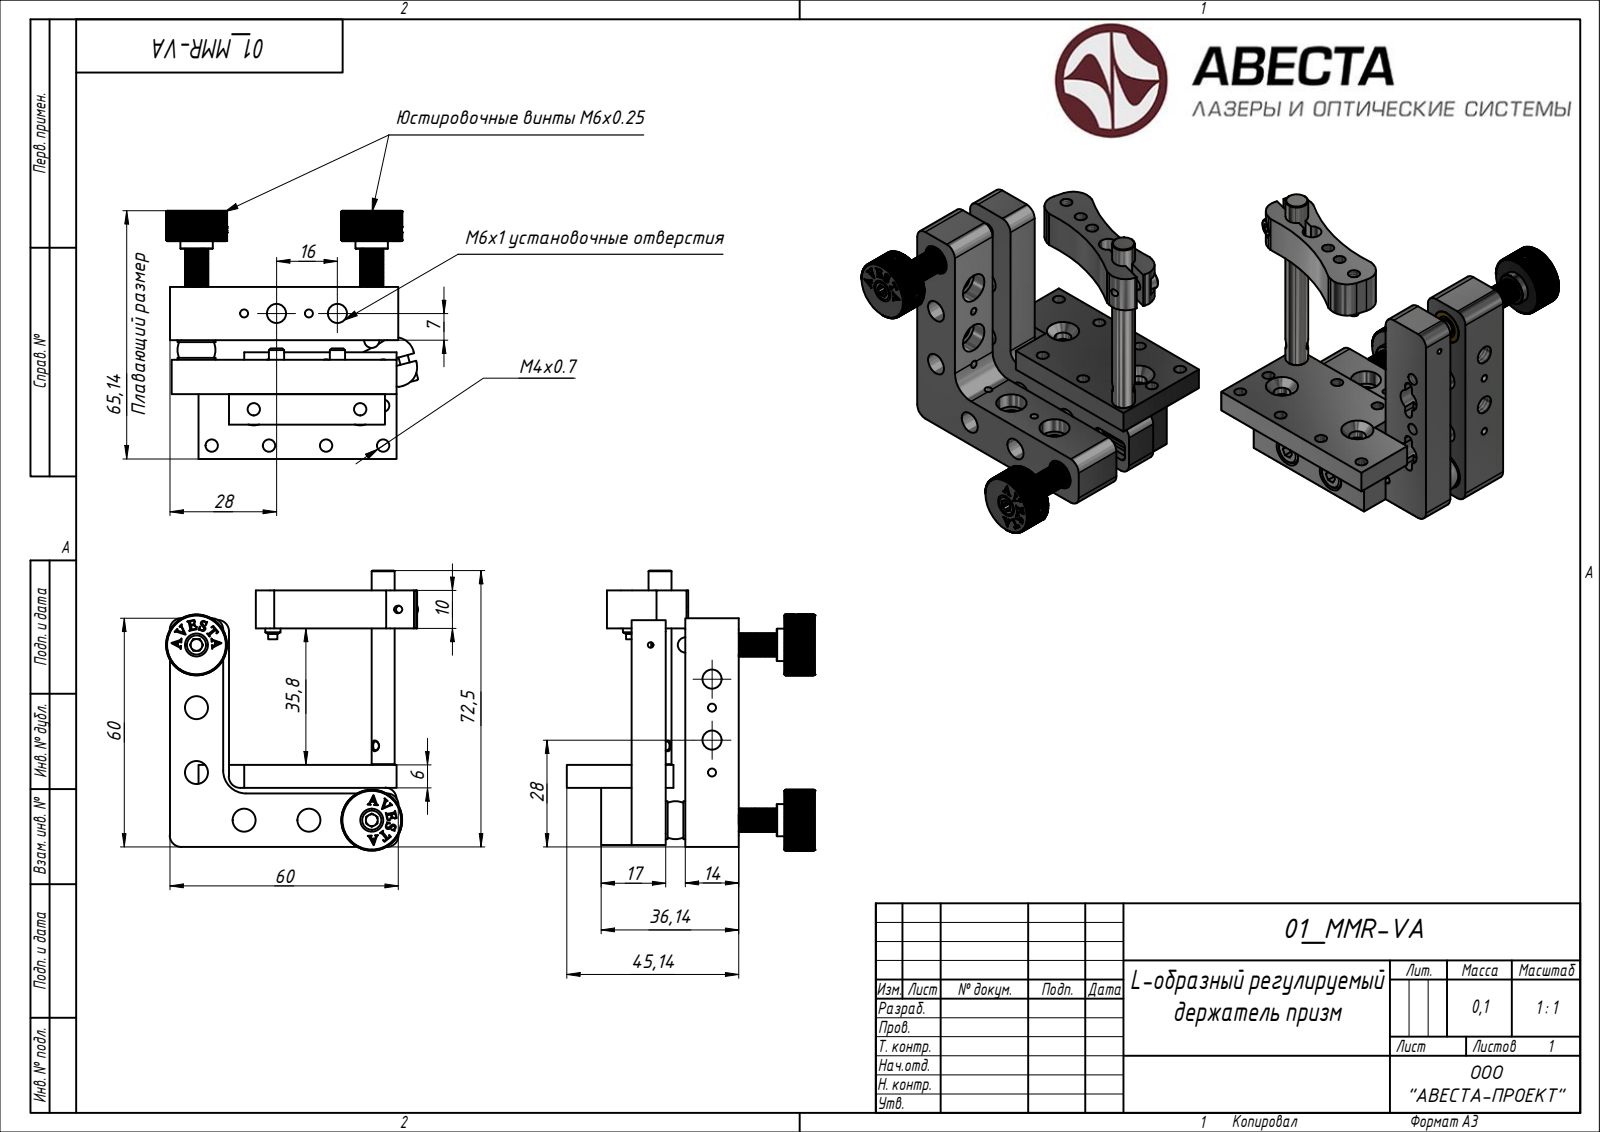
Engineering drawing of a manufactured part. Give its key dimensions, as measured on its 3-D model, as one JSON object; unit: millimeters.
{"part_name": "01_MMR-VA; 60x60_base; 60x60 держатель призм holder; конусная пятка d10 (+8 more)", "step_written_by": "Autodesk Inventor 2020 (AUTOMOTIVE_DESIGN)", "units": "millimeters", "bodies": {"solids": 22, "faces": 1920, "planar": 1134, "cylindrical": 604, "other": 182}, "overall_size": [88.26, 84.27, 73.17], "volume_mm3": 50965, "surface_area_mm2": 35055, "round_holes": [[3.24, 13], [6, 10], [5, 9], [8, 8], [1.57, 4], [2.05, 4], [3.2, 4], [4.5, 4], [3.1, 2], [5.46, 2], [9, 2], [10, 2]], "round_bosses_or_shafts": [[4, 4], [8.5, 2], [8, 2], [7, 2], [6, 2], [4.5, 1], [3.5, 1], [2.5, 1]], "partial_cylinders_radius": [[1.25, 12], [3, 11], [5, 4], [8, 2], [47.5, 2], [2.5, 1], [6, 1]], "face_to_face_distances": [14, 14.14, 5.14, 28.14, 9, 6, 19.14, 15, 1.5, 8], "hole_center_spacings": [16, 46, 9.12, 25.04, 51.93, 60.21, 17, 8.5]}
